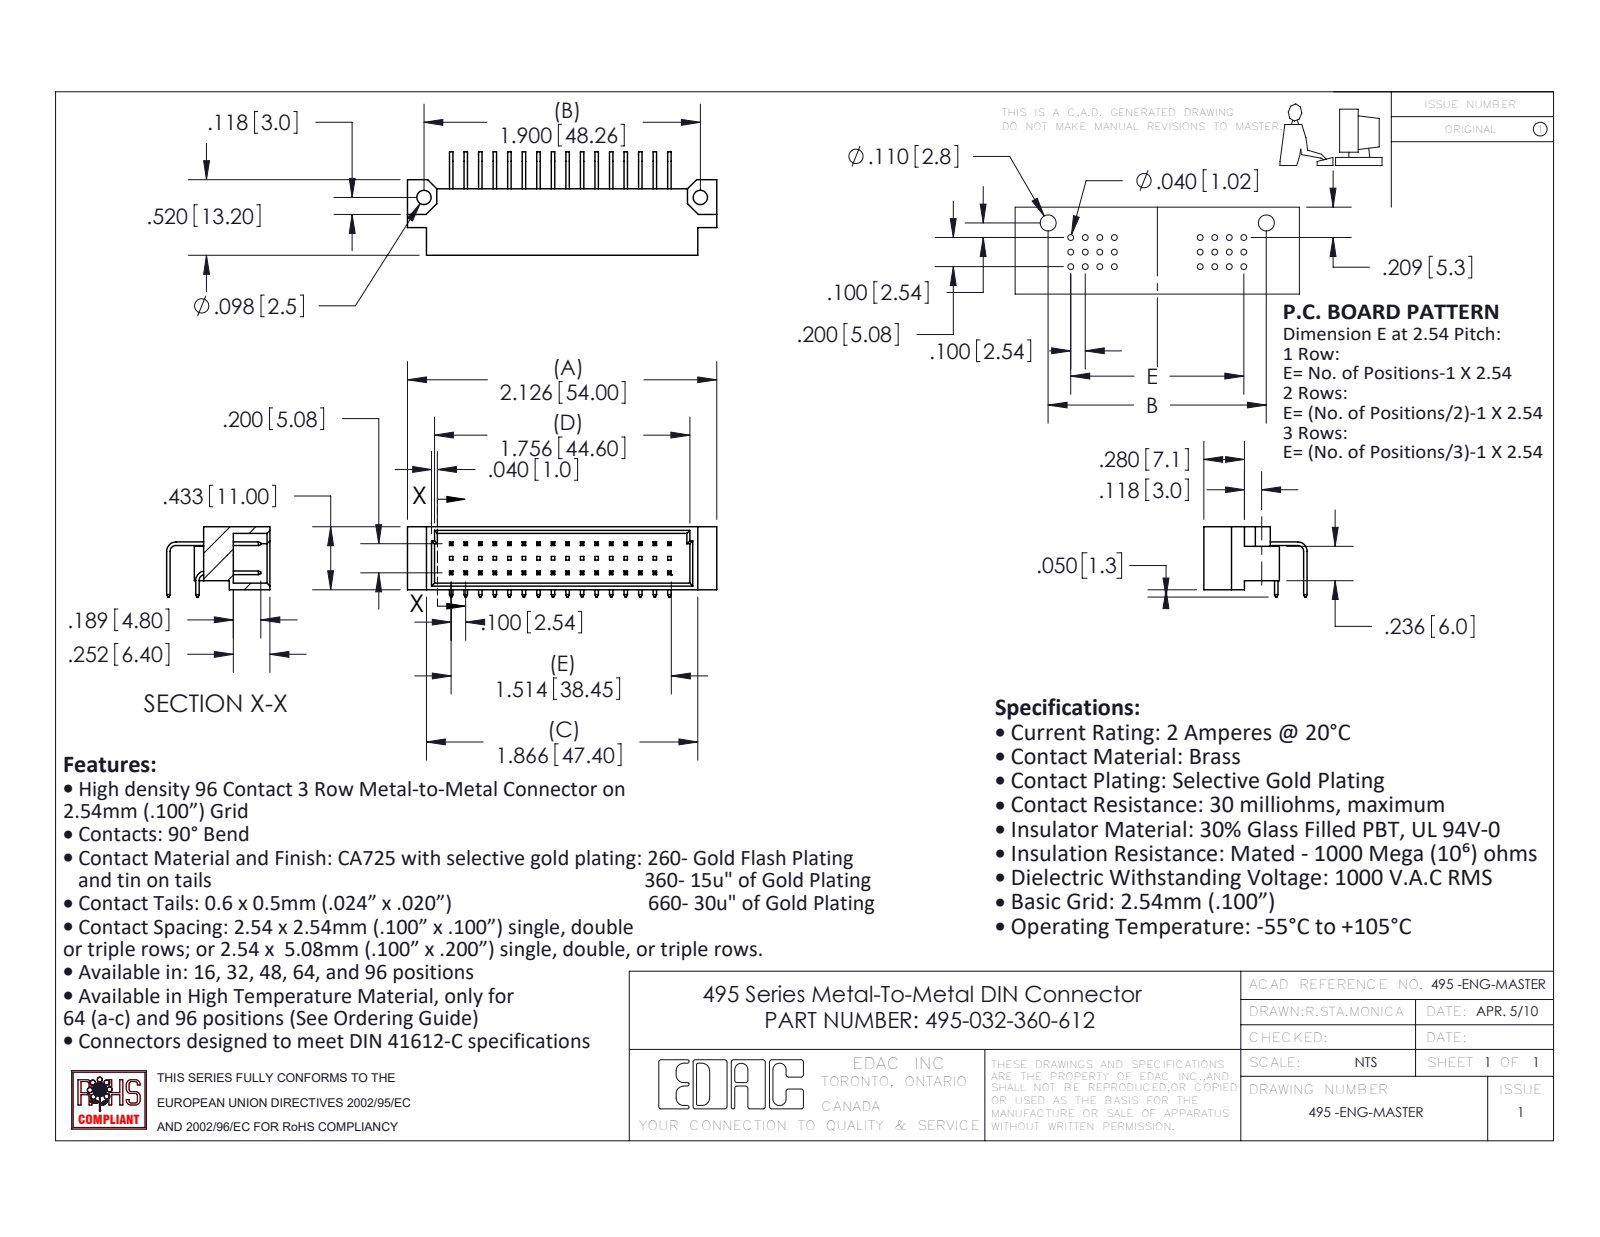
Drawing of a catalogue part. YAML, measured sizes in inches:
part_name: "495-290-3; 495-290-1; 495-032-360-612; 495 Part_48"
step_written_by: "SolidWorks 2020 (AUTOMOTIVE_DESIGN)"
units: inches
bodies: {solids: 33, faces: 818, planar: 750, cylindrical: 68, other: 0}
overall_size: [2.126, 0.711, 0.483]
volume: 0.225
surface_area: 8.519
round_holes:
  - {diameter: 0.098, count: 2}
partial_cylinders:
  - {radius: 0.04, count: 2}
  - {radius: 0.065, count: 2}
face_to_face_distances: [0.2, 0.1, 0.045, 0.388, 0.024, 0.205, 0.433, 0.3, 0.063, 0.4]
hole_center_spacings: [1.9]
